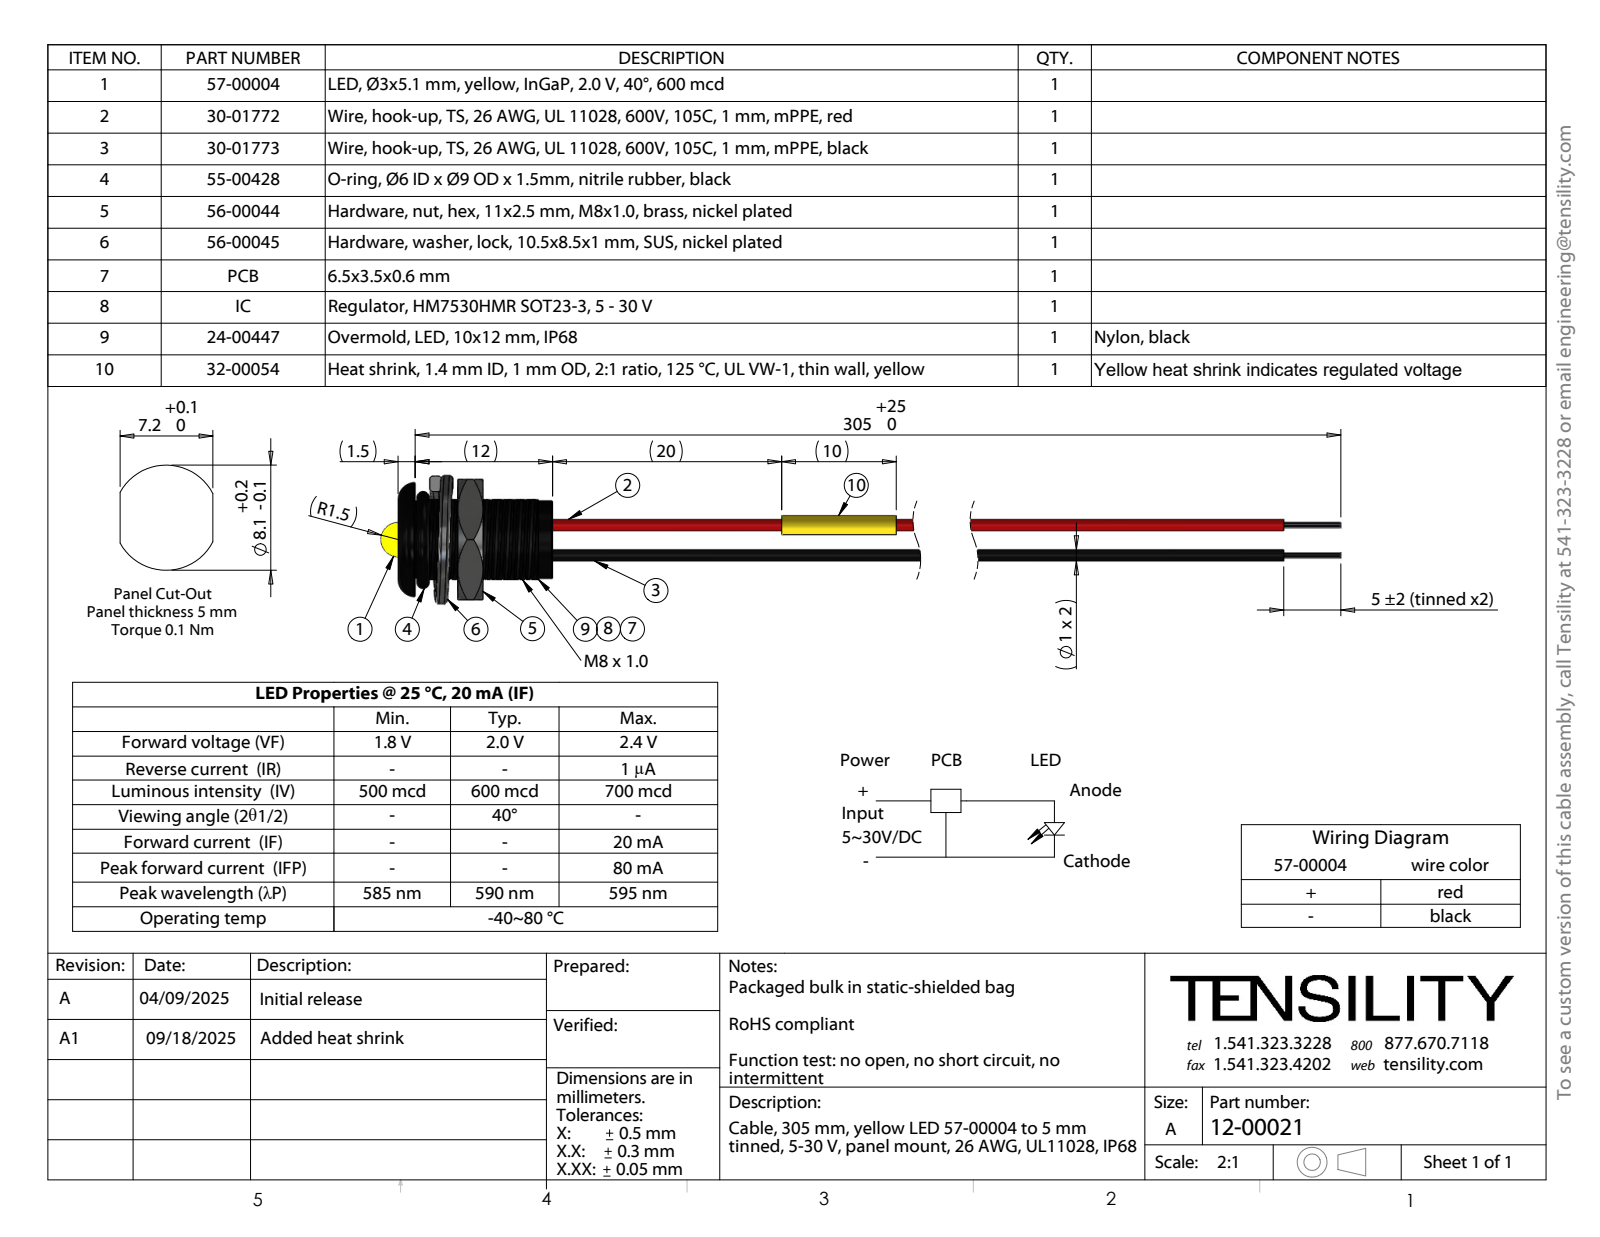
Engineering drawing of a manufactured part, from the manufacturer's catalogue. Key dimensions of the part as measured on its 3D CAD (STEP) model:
Part name (STEP PRODUCT): 24-00447; 55-00428; 57-00004_trimmed leads; 30-01773_stripped and tinned (+4 more)
STEP written by: SolidWorks 2021 (CONFIG_CONTROL_DESIGN)
Units: millimetres
Bodies: 57 solids, 555 faces (186 planar, 246 cylindrical, 123 other)
Overall size (bounding box): 169.99 × 12.12 × 11.21
Volume: 1 005 mm³ · Surface area: 5 908 mm²
Round holes (diameter × count): ⌀1 ×2
Round bosses / shafts (diameter × count): ⌀1 ×2, ⌀0.5 ×2, ⌀6.8 ×1, ⌀3 ×1
Partial cylindrical surfaces — rounded edges, fillets, slot ends (radius × count): R3.48 ×1, R4 ×1
Main face-to-face distances: 1.5, 13.5, 12, 10.5, 5.21, 3.71, 8.29, 7.41, 5.91, 2.2
Hole centre spacings: 0.36, 0.38, 0.33, 2.48, 2.52, 2.43, 2.44, 2.56
